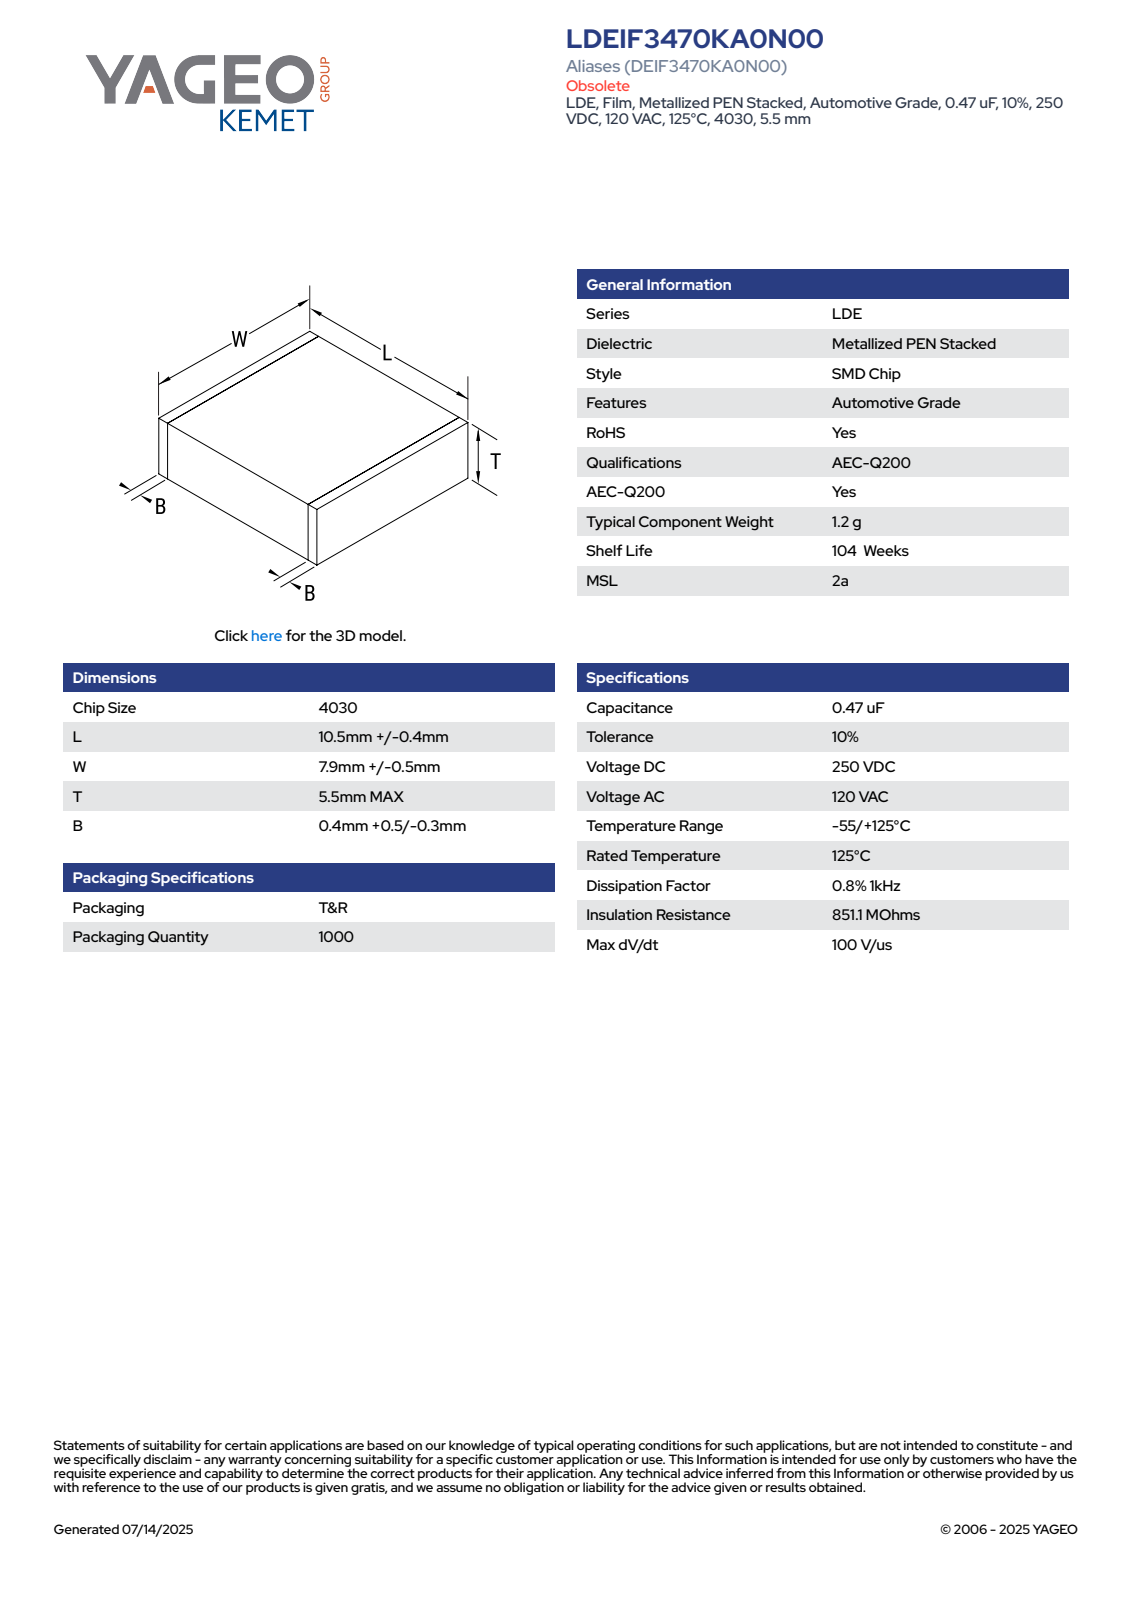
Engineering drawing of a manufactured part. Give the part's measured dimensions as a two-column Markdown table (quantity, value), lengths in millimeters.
| quantity | value |
| --- | --- |
| part name | CFS_LDELDB_4030_L10.9W8.4T5.5B0.9 |
| STEP written by | SolidWorks 2020 (AUTOMOTIVE_DESIGN) |
| units | millimeters |
| bodies | 4 solids, 73 faces (73 planar, 0 cylindrical, 0 other) |
| overall size | 10.9 × 8.4 × 5.5 |
| volume | 501 mm³ |
| surface area | 401 mm² |
| main face-to-face distances | 5.48, 8.38, 10.9, 5.49, 8.39, 5.5, 8.4, 0.5, 10.4, 9.9 |
